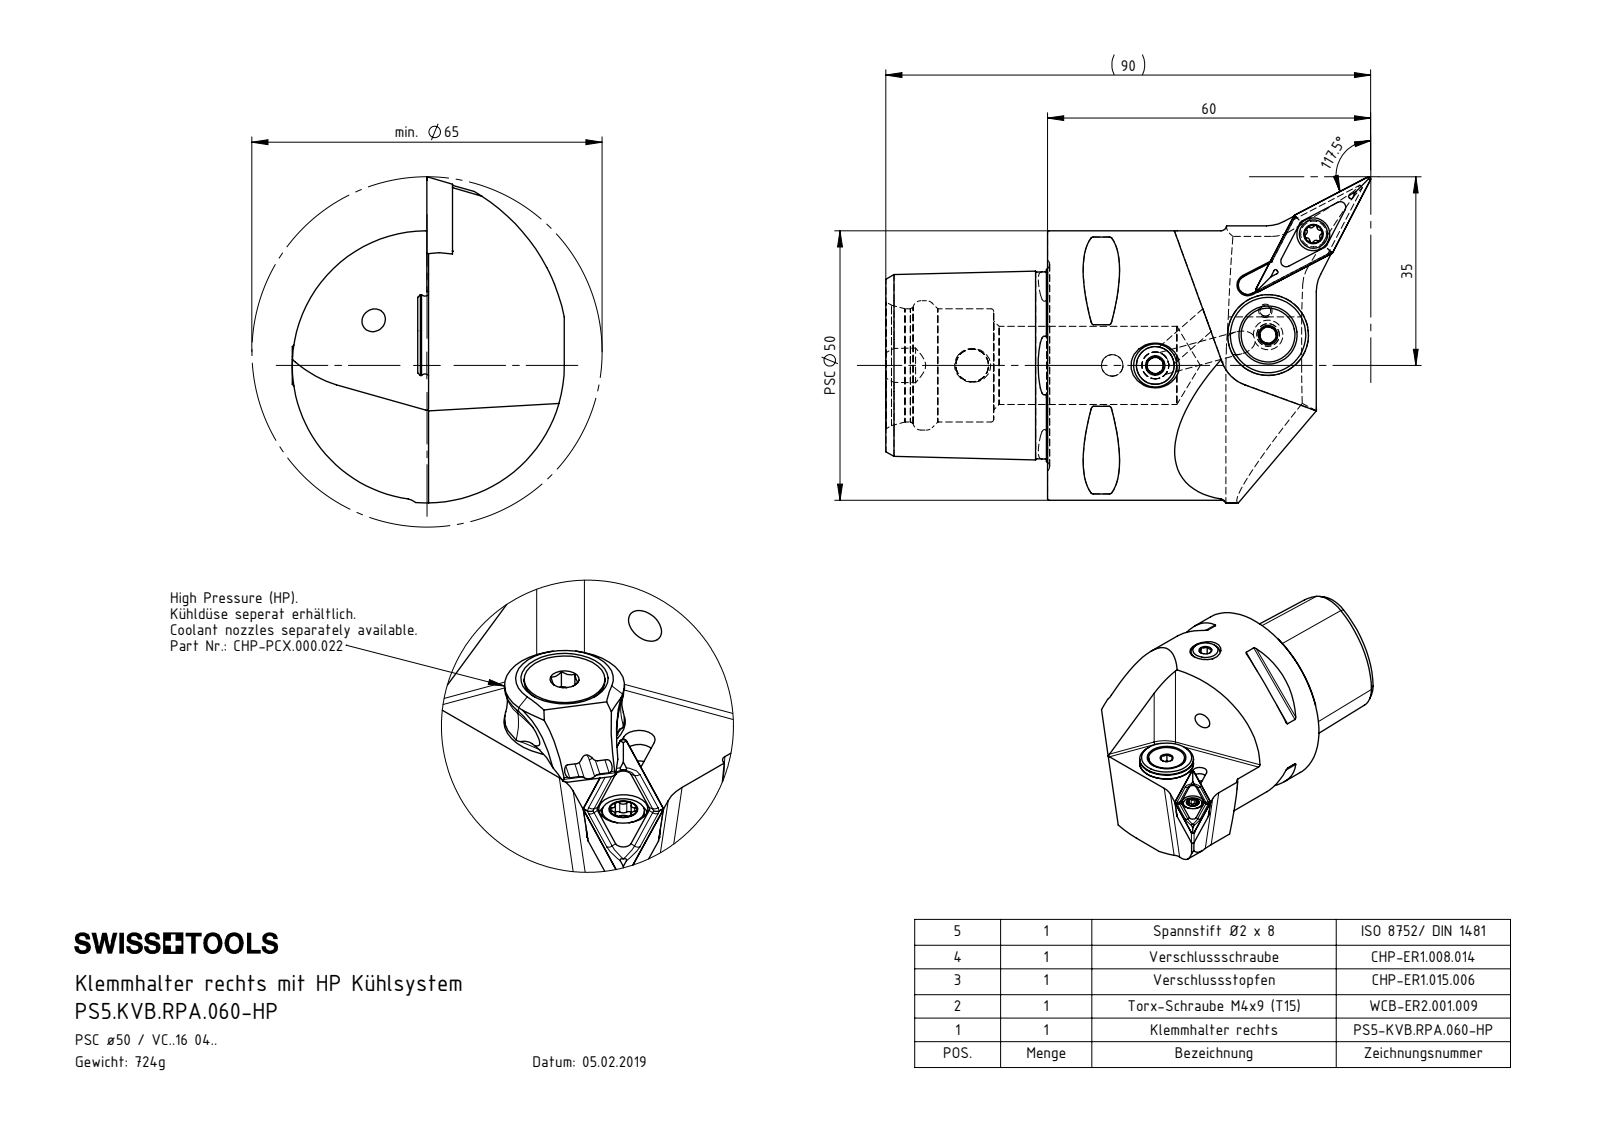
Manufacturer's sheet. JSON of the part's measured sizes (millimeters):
{"part_name": "ISO 8752 2x8; DIN 3771 - 13x1; CHP-ER1.008.014_A; WCB-ER2.001.009_A (+6 more)", "step_written_by": "SolidWorks 2017 (AUTOMOTIVE_DESIGN)", "units": "millimeters", "bodies": {"solids": 8, "faces": 279, "planar": 94, "cylindrical": 63, "other": 122}, "overall_size": [90, 60.5, 50.5], "volume_mm3": 91716, "surface_area_mm2": 21647, "round_holes": [[4.2, 3], [6.1, 2], [1.2, 1], [2, 1], [2.5, 1], [3, 1], [3.3, 1], [4, 1], [4.4, 1], [5, 1], [5.2, 1], [7, 1]], "round_bosses_or_shafts": [[50, 1], [15, 1], [13.4, 1], [10, 1], [8, 1], [5.5, 1], [5.25, 1], [5, 1]], "partial_cylinders_radius": [[0.5, 10], [0.34, 6], [0.59, 6], [7, 3], [1.75, 1], [4, 1], [25.5, 1], [35, 1]], "face_to_face_distances": [30, 4.5, 4.46, 19.18, 44.4, 20.7, 20.74, 25.2, 20, 10], "hole_center_spacings": [4.5, 8, 16.78, 16.84, 20.49, 20.54, 21.69, 22.8]}
